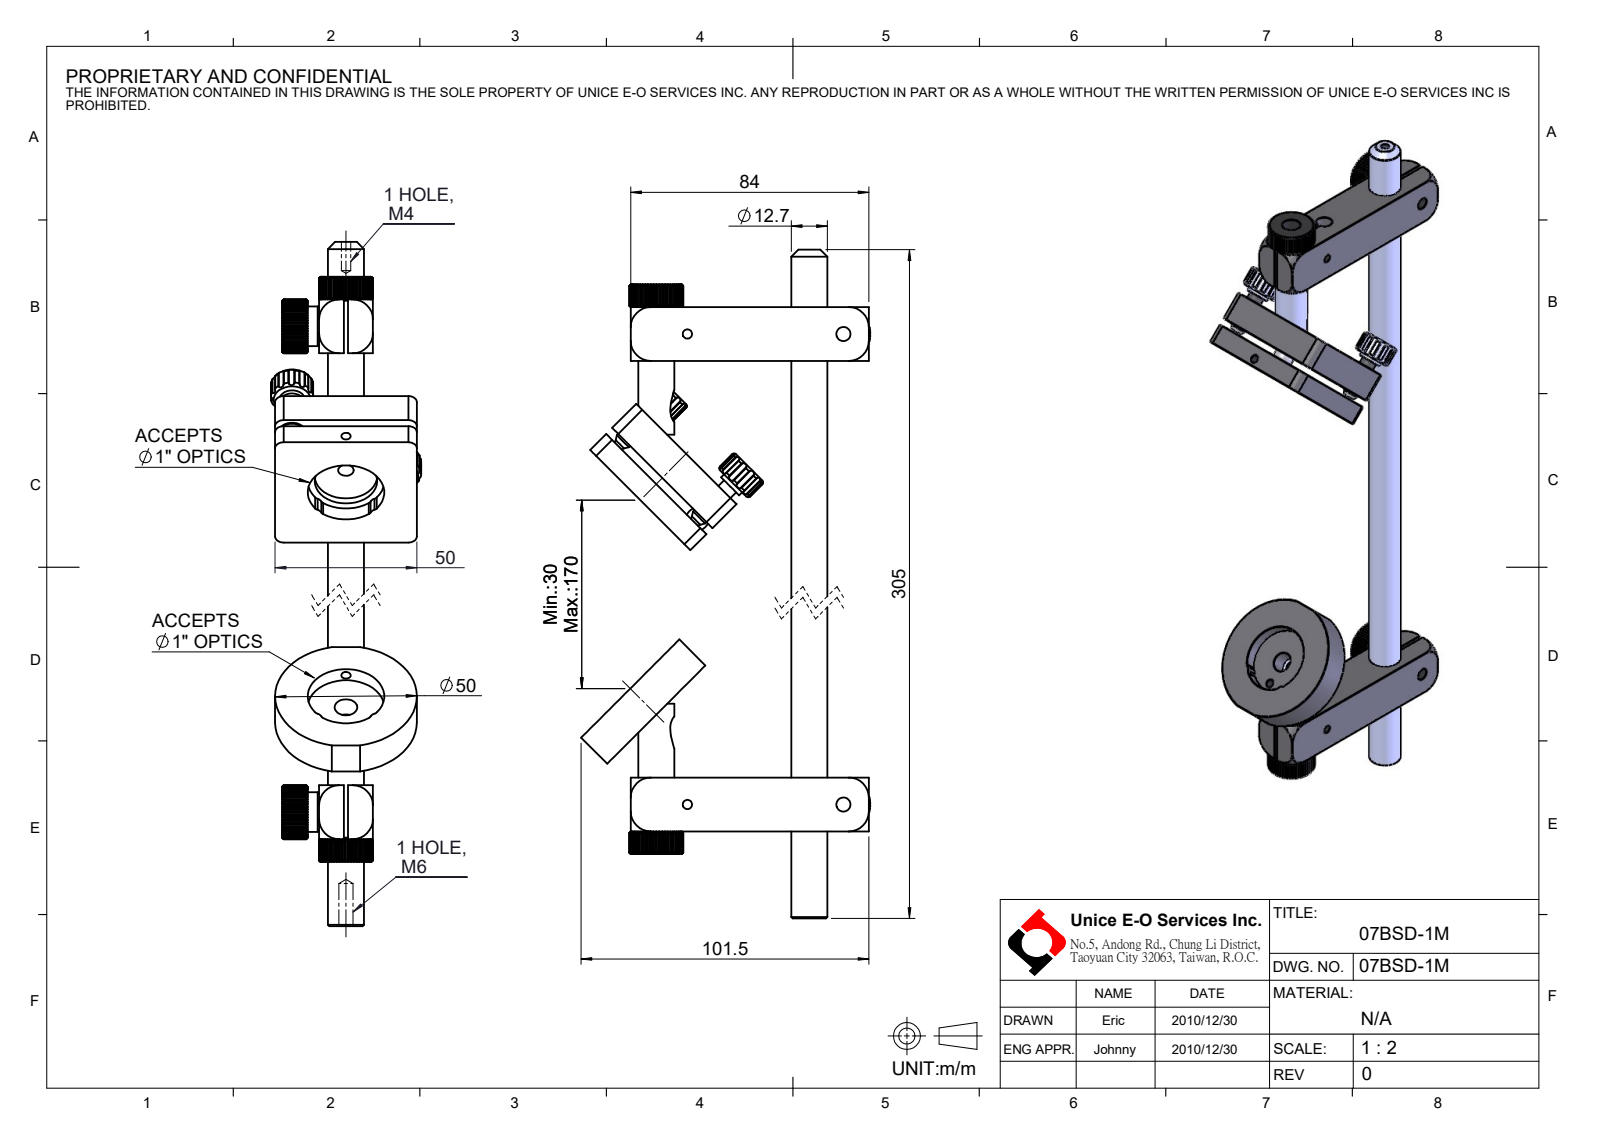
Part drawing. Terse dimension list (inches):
name: 07BSD-1M
written by: SolidWorks 2016 (CONFIG_CONTROL_DESIGN)
unit: in
bodies: 24 solids, 1670 faces (586 planar, 534 cylindrical, 550 other)
size: 12.008 × 4.016 × 2.084
volume: 10.45 in³; area: 107.2 in²
holes: 8× ⌀0.13, 4× ⌀0.067, 4× ⌀0.177, 4× ⌀0.276, 4× ⌀0.315, 3× ⌀0.197, 3× ⌀0.256, 2× ⌀0.157, 2× ⌀0.185, 2× ⌀0.232, 2× ⌀0.236, 2× ⌀0.374
bosses: 2× ⌀0.551, 2× ⌀0.374, 2× ⌀0.354, 2× ⌀0.236, 2× ⌀0.059, 1× ⌀1.969
rounds: 48× R0.012, 25× R0.059, 8× R0.079, 6× R0.118, 4× R0.03, 4× R0.098, 3× R0.374, 2× R0.295
face distances: 0.748, 0.315, 9.256, 0.472, 0.906, 0.118, 0.433, 0.591, 0.344, 0.404
hole spacings: 0.512, 1.058, 0.784, 1.791, 0.765, 0.828, 0.591, 0.785
